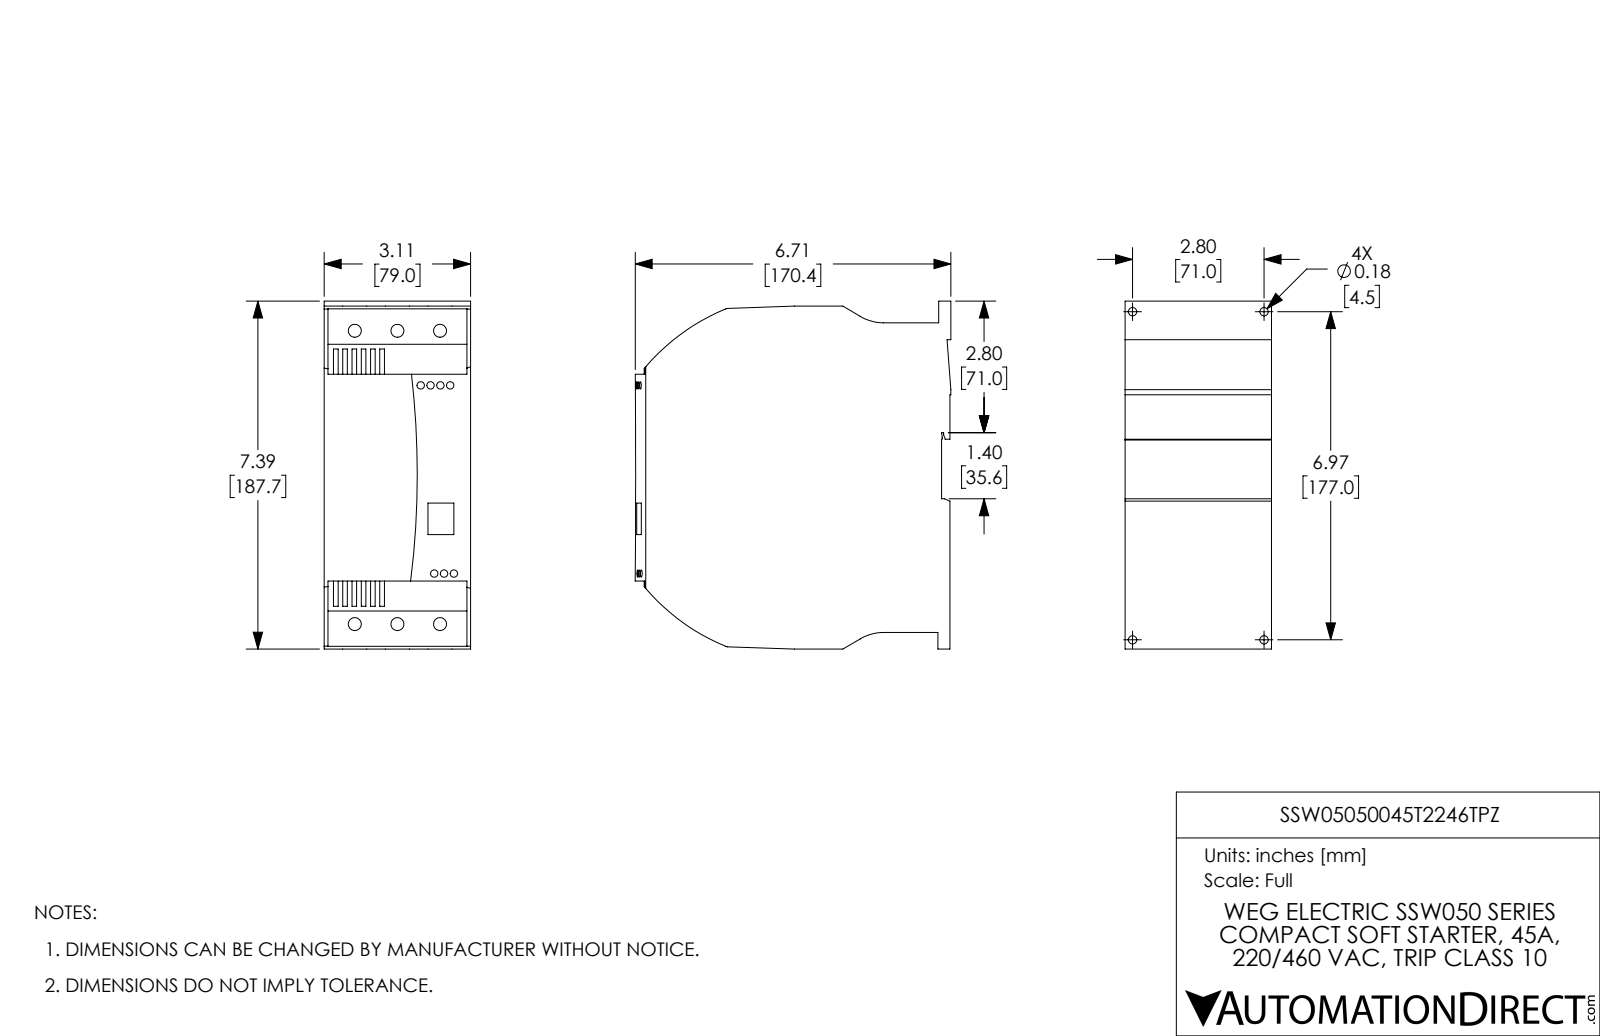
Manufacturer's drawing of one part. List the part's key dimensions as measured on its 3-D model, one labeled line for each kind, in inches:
Part name (STEP PRODUCT): SSW05 MEC B
STEP written by: SolidWorks 2017 (AUTOMOTIVE_DESIGN)
Units: inches
Bodies: 1 solid, 194 faces (149 planar, 45 cylindrical, 0 other)
Overall size (bounding box): 7.391 × 6.708 × 3.11
Volume: 127.8 in³ · Surface area: 229.1 in²
Round holes (diameter × count): ⌀0.157 ×7, ⌀0.276 ×6, ⌀0.177 ×4
Partial cylindrical surfaces — rounded edges, fillets, slot ends (radius × count): R0.098 ×2, R0.984 ×2, R4.437 ×2, R5.117 ×1, R15.153 ×1, R18.205 ×1
Main face-to-face distances: 3.11, 0.197, 0.098, 0.295, 0.394, 0.492, 0.591, 0.787, 0.689, 0.886
Hole centre spacings: 0.209, 0.906, 6.294, 0.417, 3.997, 4.006, 6.228, 0.595
